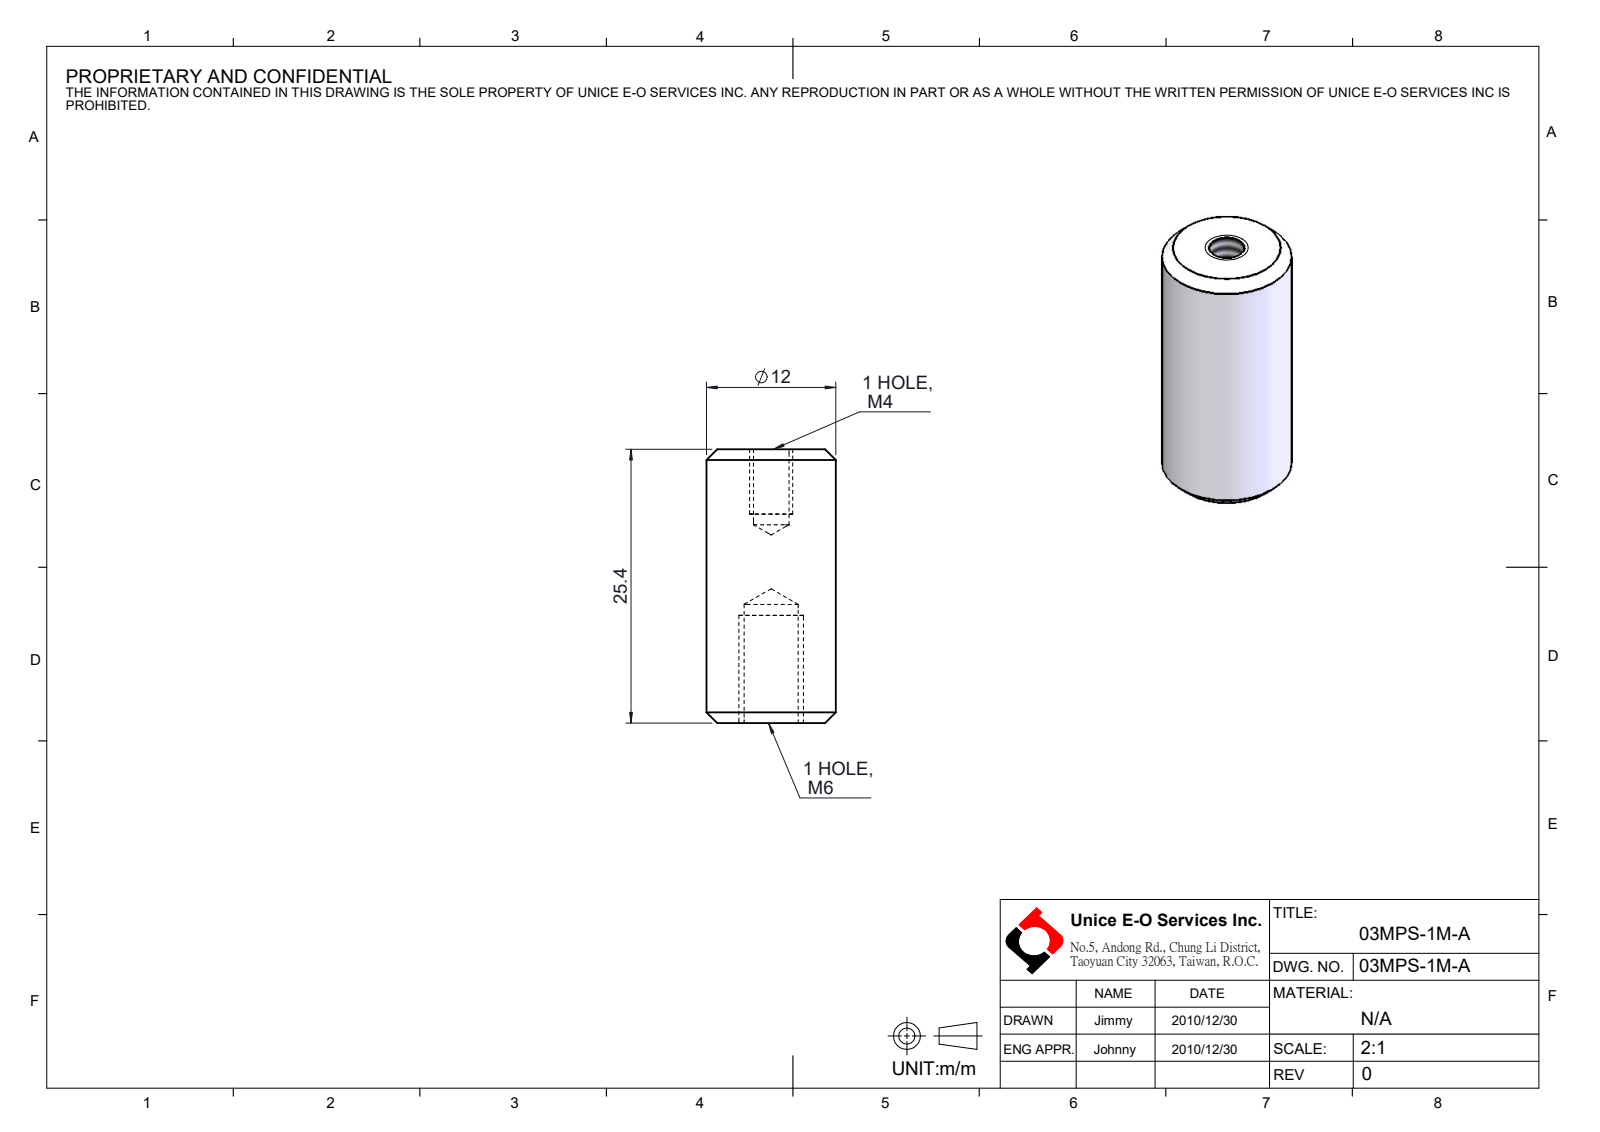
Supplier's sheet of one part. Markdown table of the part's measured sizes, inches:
| quantity | value |
| --- | --- |
| part name | 03MPS-1M-A |
| STEP written by | SolidWorks 2016 (CONFIG_CONTROL_DESIGN) |
| units | inches |
| bodies | 1 solid, 16 faces (2 planar, 6 cylindrical, 8 other) |
| overall size | 1 × 0.472 × 0.472 |
| volume | 0.156 in³ |
| surface area | 2.15 in² |
| round holes (diameter × count) | 0.13 × 1, 0.197 × 1 |
| round bosses / shafts (diameter × count) | 0.472 × 1 |
| main face-to-face distances | 1 |
